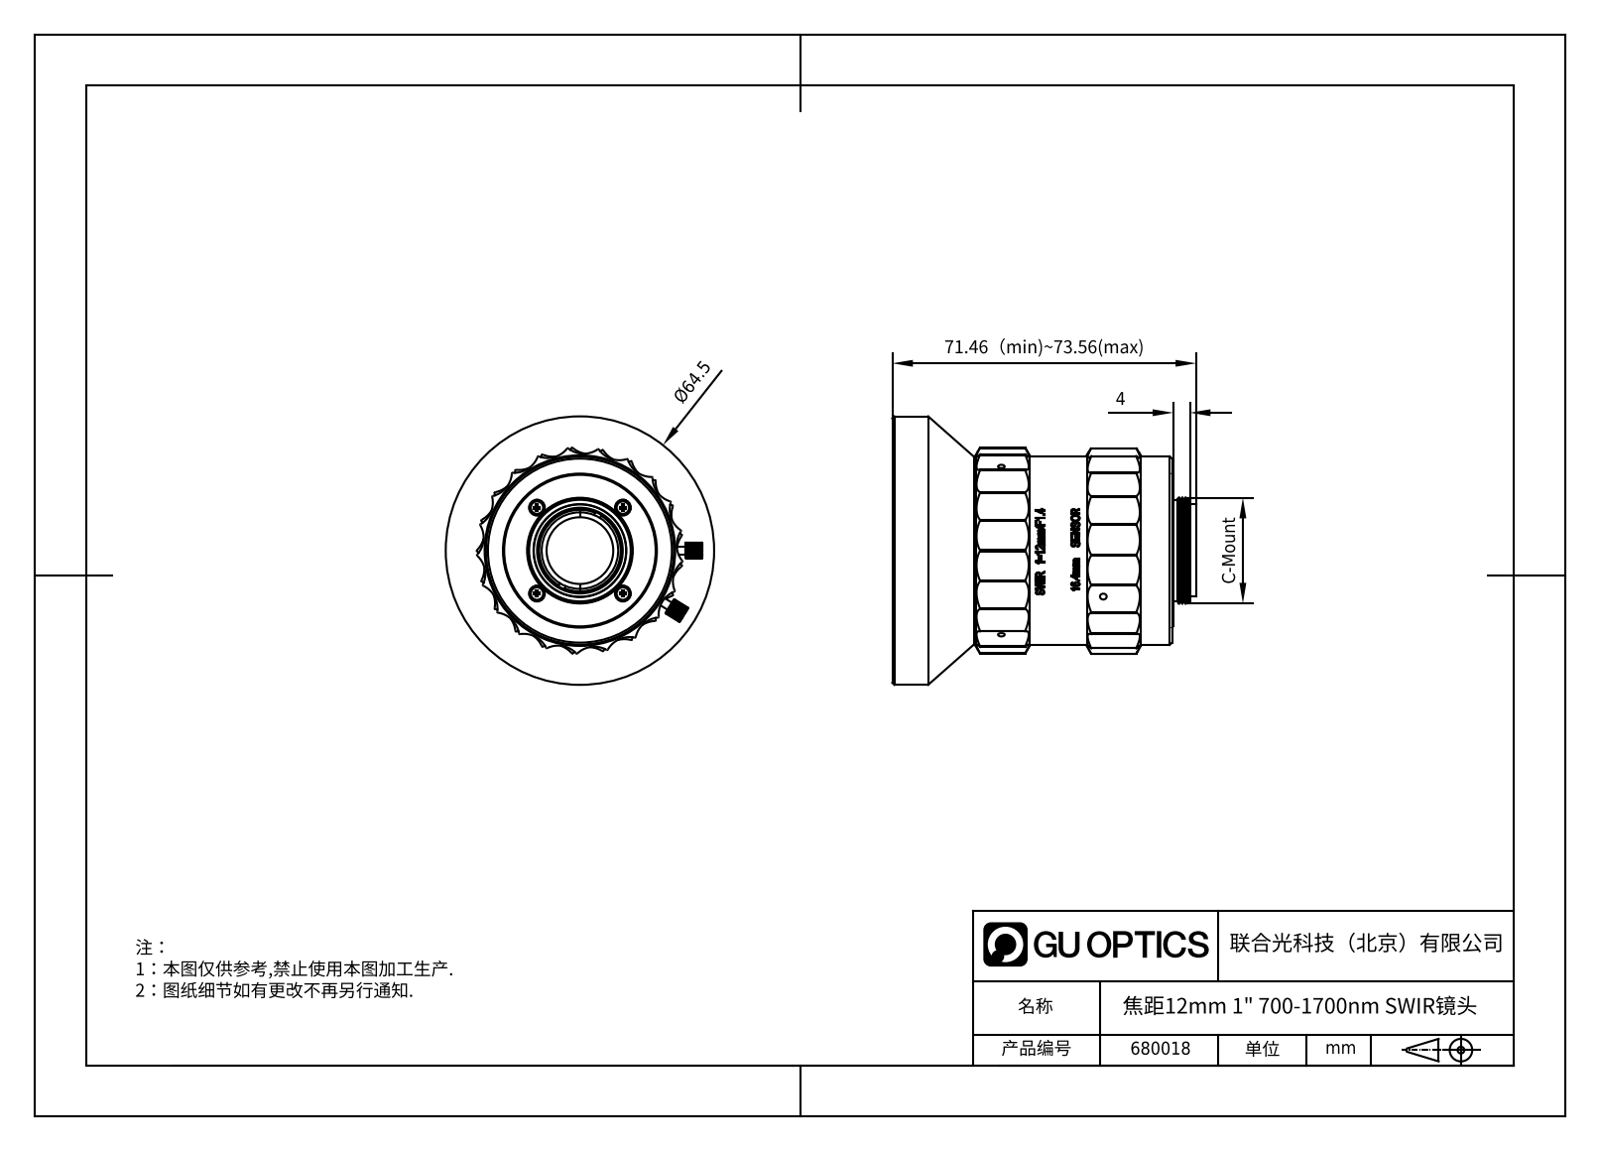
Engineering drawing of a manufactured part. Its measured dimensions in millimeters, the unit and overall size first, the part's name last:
Units: millimetres
Overall size (bounding box): 85.05 × 64.5 × 64.5
Round holes (diameter × count): ⌀1.6 ×12, ⌀1.2 ×10, ⌀2.2 ×4, ⌀3.8 ×4, ⌀0.9 ×3, ⌀0.5 ×2, ⌀2.8 ×2, ⌀1.3 ×1, ⌀1.4 ×1, ⌀1.8 ×1, ⌀2.6 ×1, ⌀2.7 ×1
Round bosses / shafts (diameter × count): ⌀2 ×6, ⌀3.6 ×4, ⌀2.5 ×2, ⌀1.7 ×2, ⌀64.5 ×1, ⌀48 ×1, ⌀45.2 ×1, ⌀40.9 ×1
Partial cylindrical surfaces — rounded edges, fillets, slot ends (radius × count): R0.2 ×42, R6 ×42, R2 ×3, R0.3 ×2, R1.1 ×2, R1.25 ×2, R1 ×1, R12.25 ×1
Main face-to-face distances: 11.2, 0.47, 3.5, 41.4, 60.72, 42.3, 0.9, 10.8, 30.6, 31.5
Hole centre spacings: 9.9, 16.02, 11.64, 18.84, 6.11, 6.12, 14.59, 18
Volume: 81 766 mm³ · Surface area: 56 195 mm²
Bodies: 26 solids, 1401 faces (588 planar, 354 cylindrical, 459 other)
Part name (STEP PRODUCT): 680018
STEP written by: SolidWorks 2020 (CONFIG_CONTROL_DESIGN)
